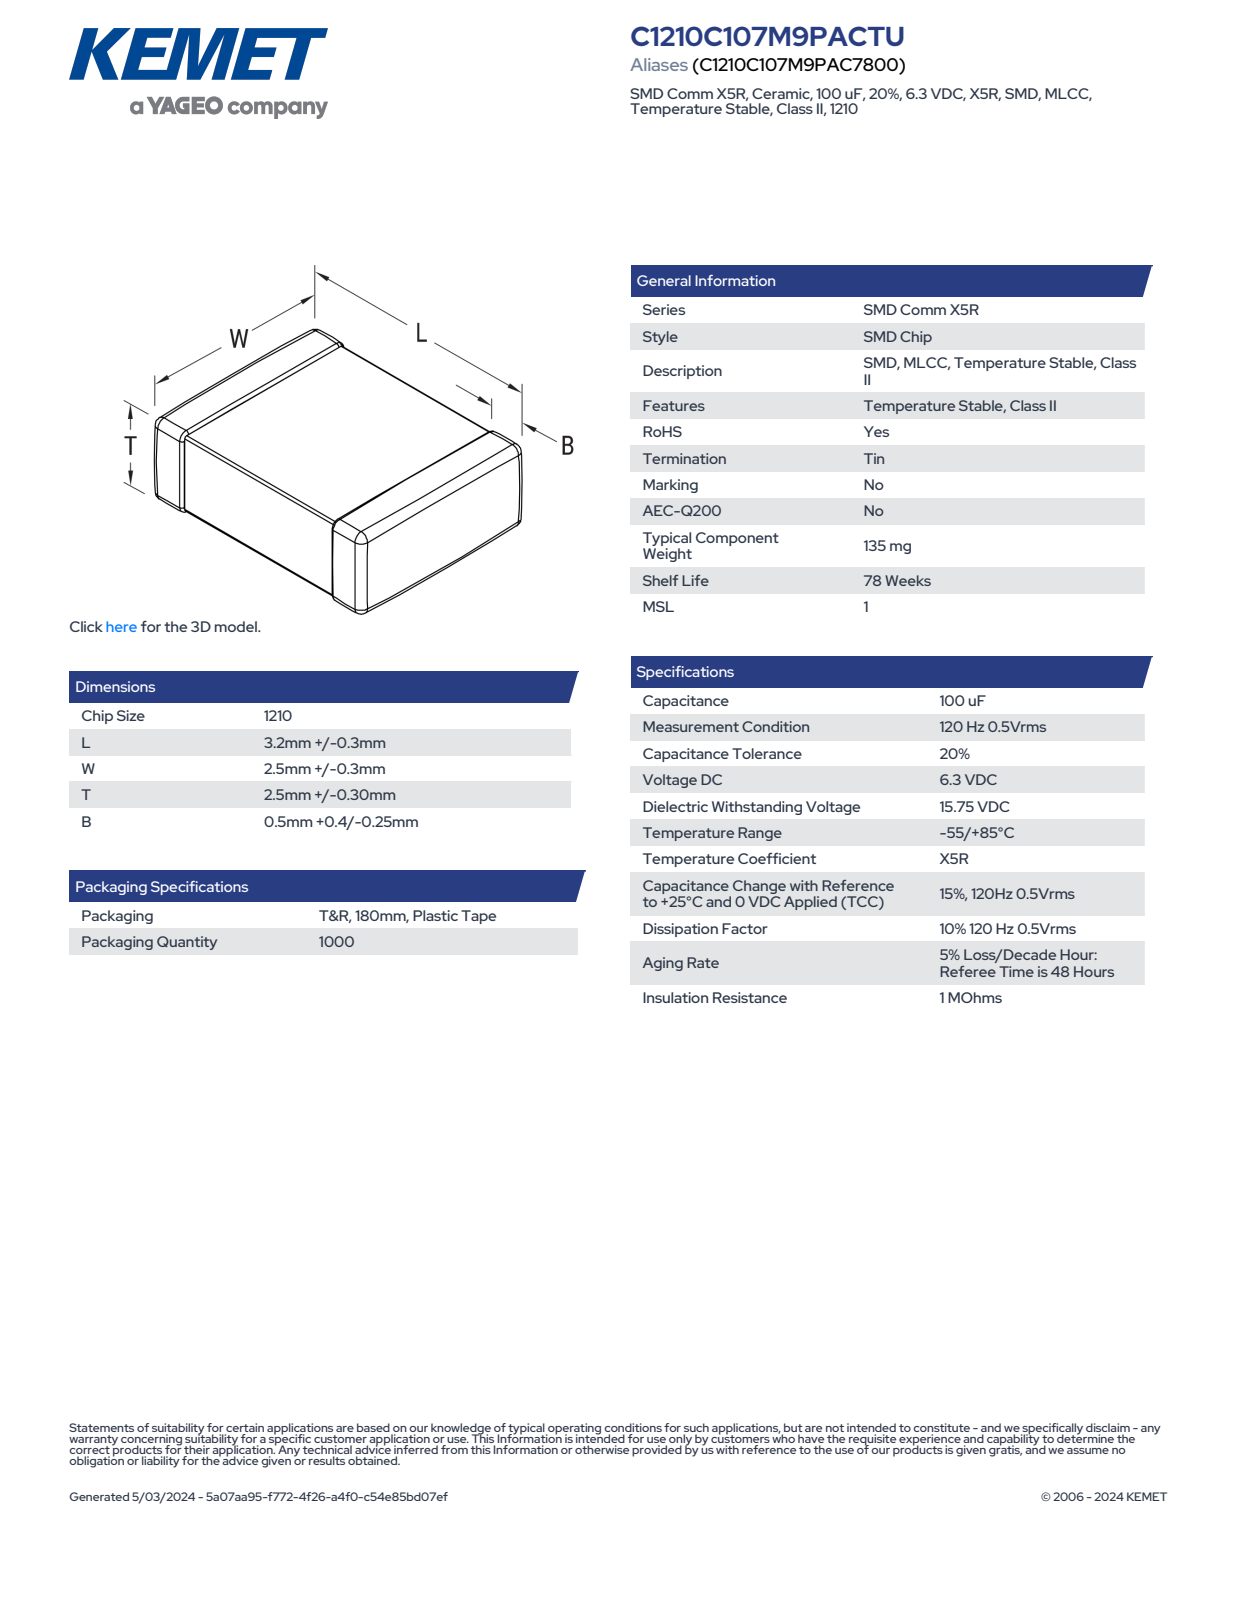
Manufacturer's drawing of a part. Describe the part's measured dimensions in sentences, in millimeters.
The part is named "CCS_CCSTD_1210_L3.5W2.8T2.8B0.5". Its 3-D file was written by "SolidWorks 2021 (AUTOMOTIVE_DESIGN)". It is 4 solids with 125 faces: 71 planar, 38 cylindrical and 16 other. Overall it measures 3.5 by 2.8 by 2.8 millimeters. Its volume is 26 cubic millimeters and its surface area 55 square millimeters. The main face-to-face distances are 2.74, 2.68, 2.8, 3.5, 2.75, 2.69, 0.41, 1.48, 2.02, 1.89.
